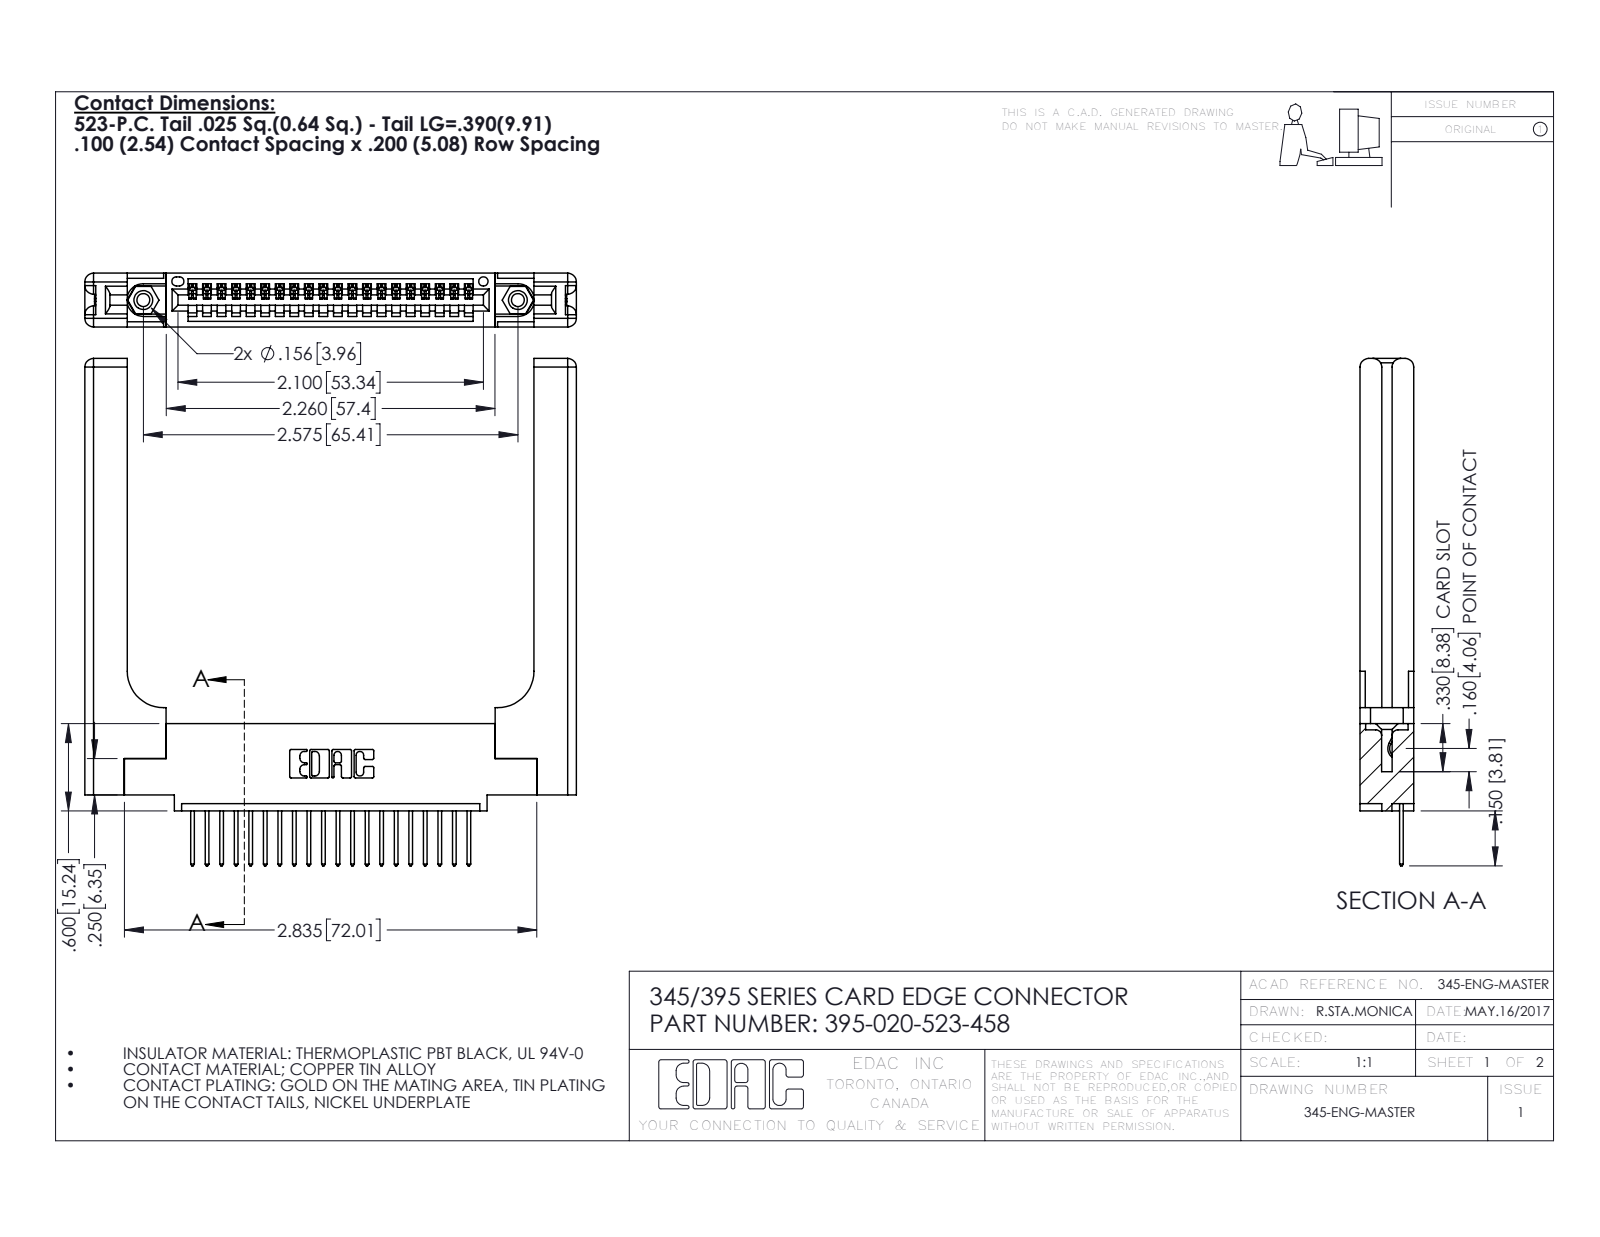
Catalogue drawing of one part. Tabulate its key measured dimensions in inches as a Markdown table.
| quantity | value |
| --- | --- |
| part name | 345 Part_0.110 Offset - 0.156 Dia-TH; 345-250-001_345-250-001-102; 345-220-058_345-220-058; 345-292-001_345-293-123 (+1 more) |
| STEP written by | SolidWorks 2016 (CONFIG_CONTROL_DESIGN) |
| units | inches |
| bodies | 25 solids, 1546 faces (1032 planar, 454 cylindrical, 60 other) |
| overall size | 3.487 × 3.379 × 0.37 |
| volume | 1.001 in³ |
| surface area | 24.17 in² |
| round holes (diameter × count) | 0.089 × 2, 0.125 × 2, 0.156 × 2, 0.064 × 1 |
| round bosses / shafts (diameter × count) | 0.155 × 2 |
| partial cylindrical surfaces (radius × count) | 0.006 × 40, 0.01 × 40, 0.01 × 22, 0.06 × 16, 0.007 × 6, 0.031 × 6, 0.026 × 3, 0.03 × 2 |
| main face-to-face distances | 0.37, 0.072, 0.298, 0.148, 0.15, 0.077, 0.22, 0.098, 0.272, 0.025 |
| hole center spacings | 0.27, 2.341, 2.575 |
